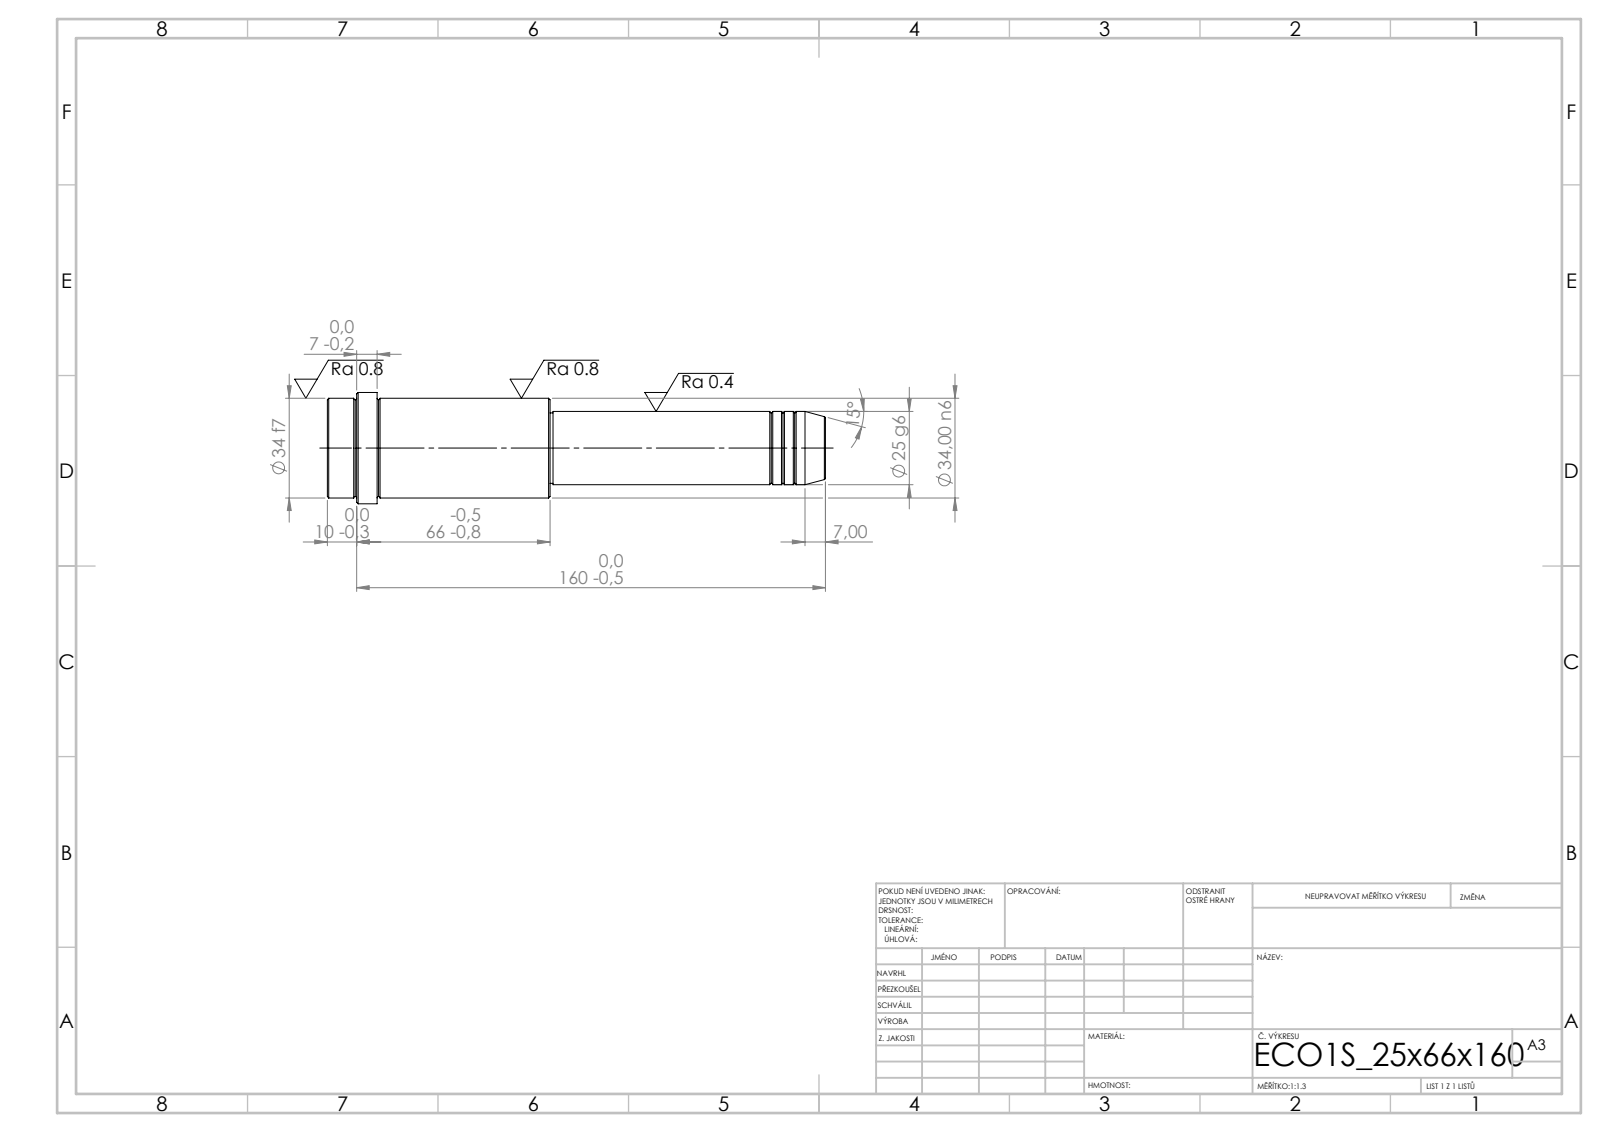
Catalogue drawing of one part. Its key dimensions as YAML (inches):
step_written_by: "SolidWorks 2019 (CONFIG_CONTROL_DESIGN)"
units: inches
bodies: {solids: 1, faces: 52, planar: 6, cylindrical: 16, other: 30}
overall_size: [6.693, 1.496, 1.496]
volume: 7.078
surface_area: 27.75
round_bosses_or_shafts:
  - {diameter: 1.496, count: 1}
  - {diameter: 1.339, count: 1}
  - {diameter: 0.984, count: 1}
  - {diameter: 0.945, count: 1}
face_to_face_distances: [2.992, 3.701, 6.693, 6.024, 2.323, 0.669, 6.299, 2.598, 0.276, 0.394]
